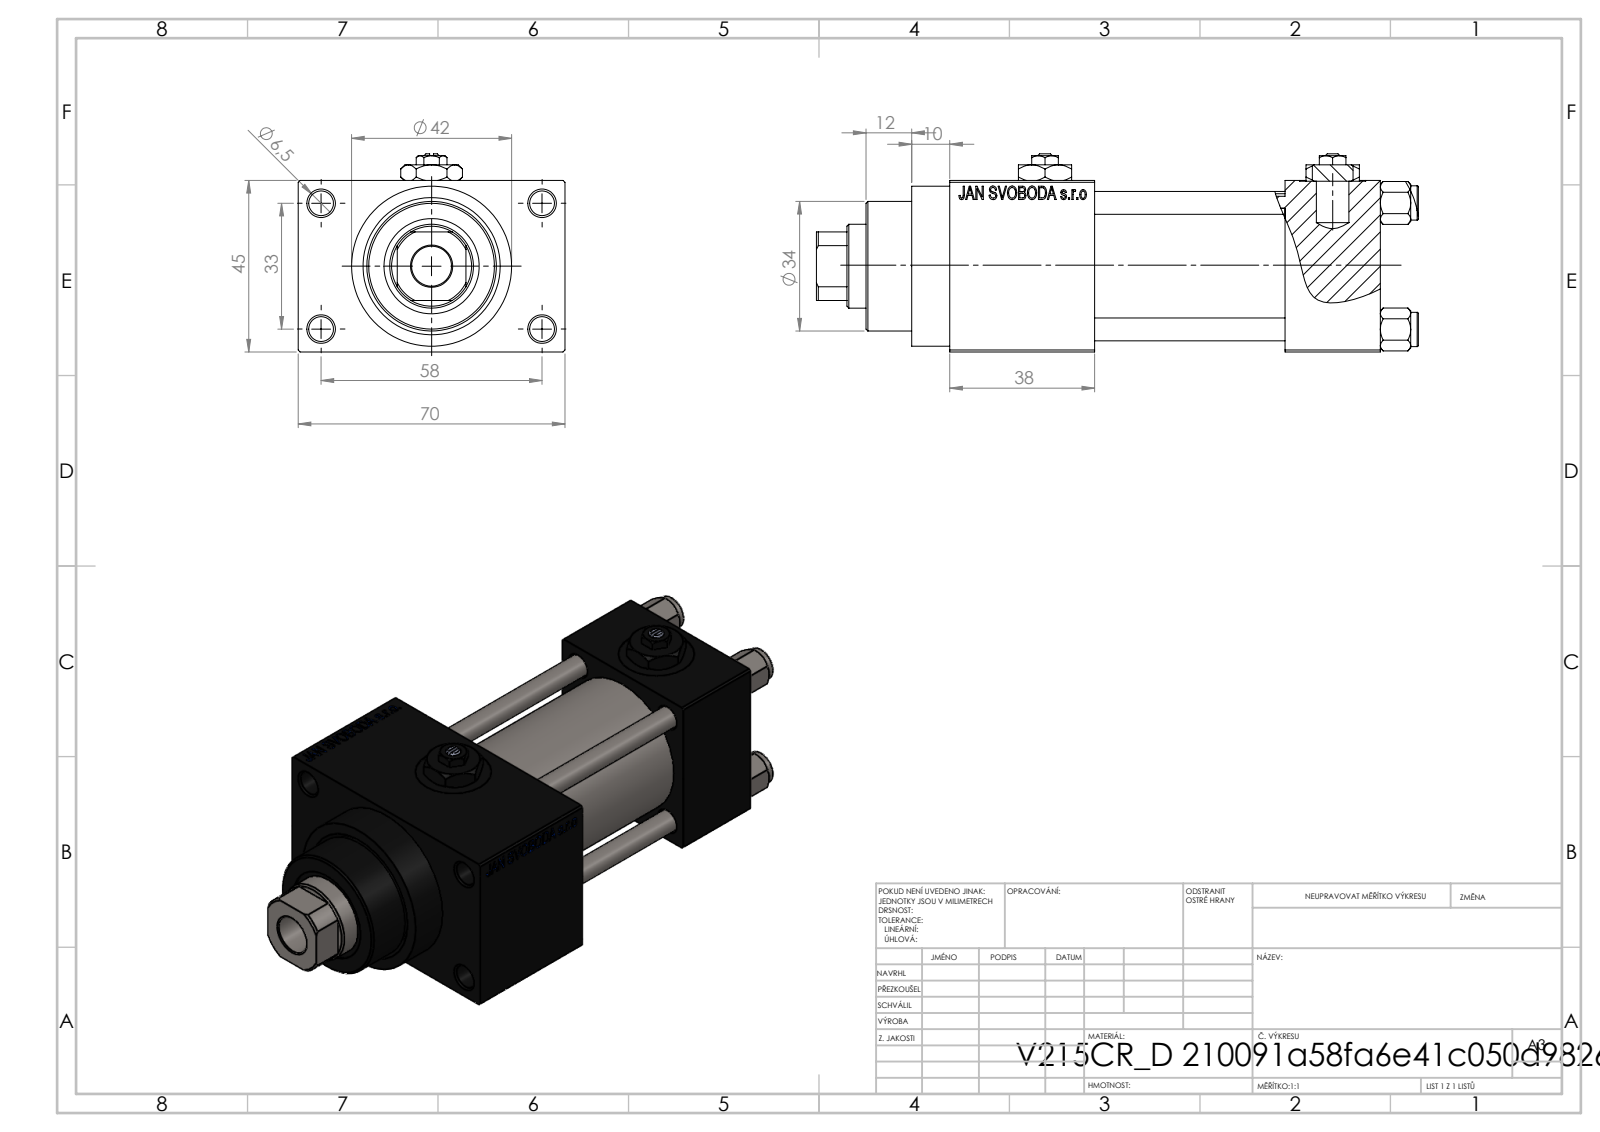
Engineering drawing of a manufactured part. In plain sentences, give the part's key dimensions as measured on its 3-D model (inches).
The part is named "Zatka_pro_OIL_PORT; V215_VC_A; V215CR_D_TYCINKA; NUT_M5_D (+2 more)". Its 3-D file was written by "SolidWorks 2019 (CONFIG_CONTROL_DESIGN)". It is 13 solids with 1204 faces: 542 planar, 100 cylindrical and 562 other. Overall it measures 6.22 by 2.756 by 2.047 inches. Its volume is 14.84 cubic inches and its surface area 125.7 square inches. Round holes: 4 of diameter 0.236, 4 of diameter 0.256, 2 of diameter 0.276, 2 of diameter 0.518, 2 of diameter 0.787, 1 of diameter 0.413, 1 of diameter 0.866, 1 of diameter 0.945, 1 of diameter 0.984, 1 of diameter 1.26, 1 of diameter 1.299. Round bosses or shafts: 4 of diameter 0.354, 1 of diameter 1.654, 1 of diameter 1.496, 1 of diameter 1.339. Partial cylindrical surfaces (rounded edges, fillets, slot ends): 1 of radius 0.413. The main face-to-face distances are 1.772, 0.984, 0.492, 2.264, 1.969, 2.953, 3.465, 2.756, 1.496, 4.449. The hole center spacings are 0.488, 0.924, 1.307, 1.314, 1.392, 1.795, 2.219, 1.299.
